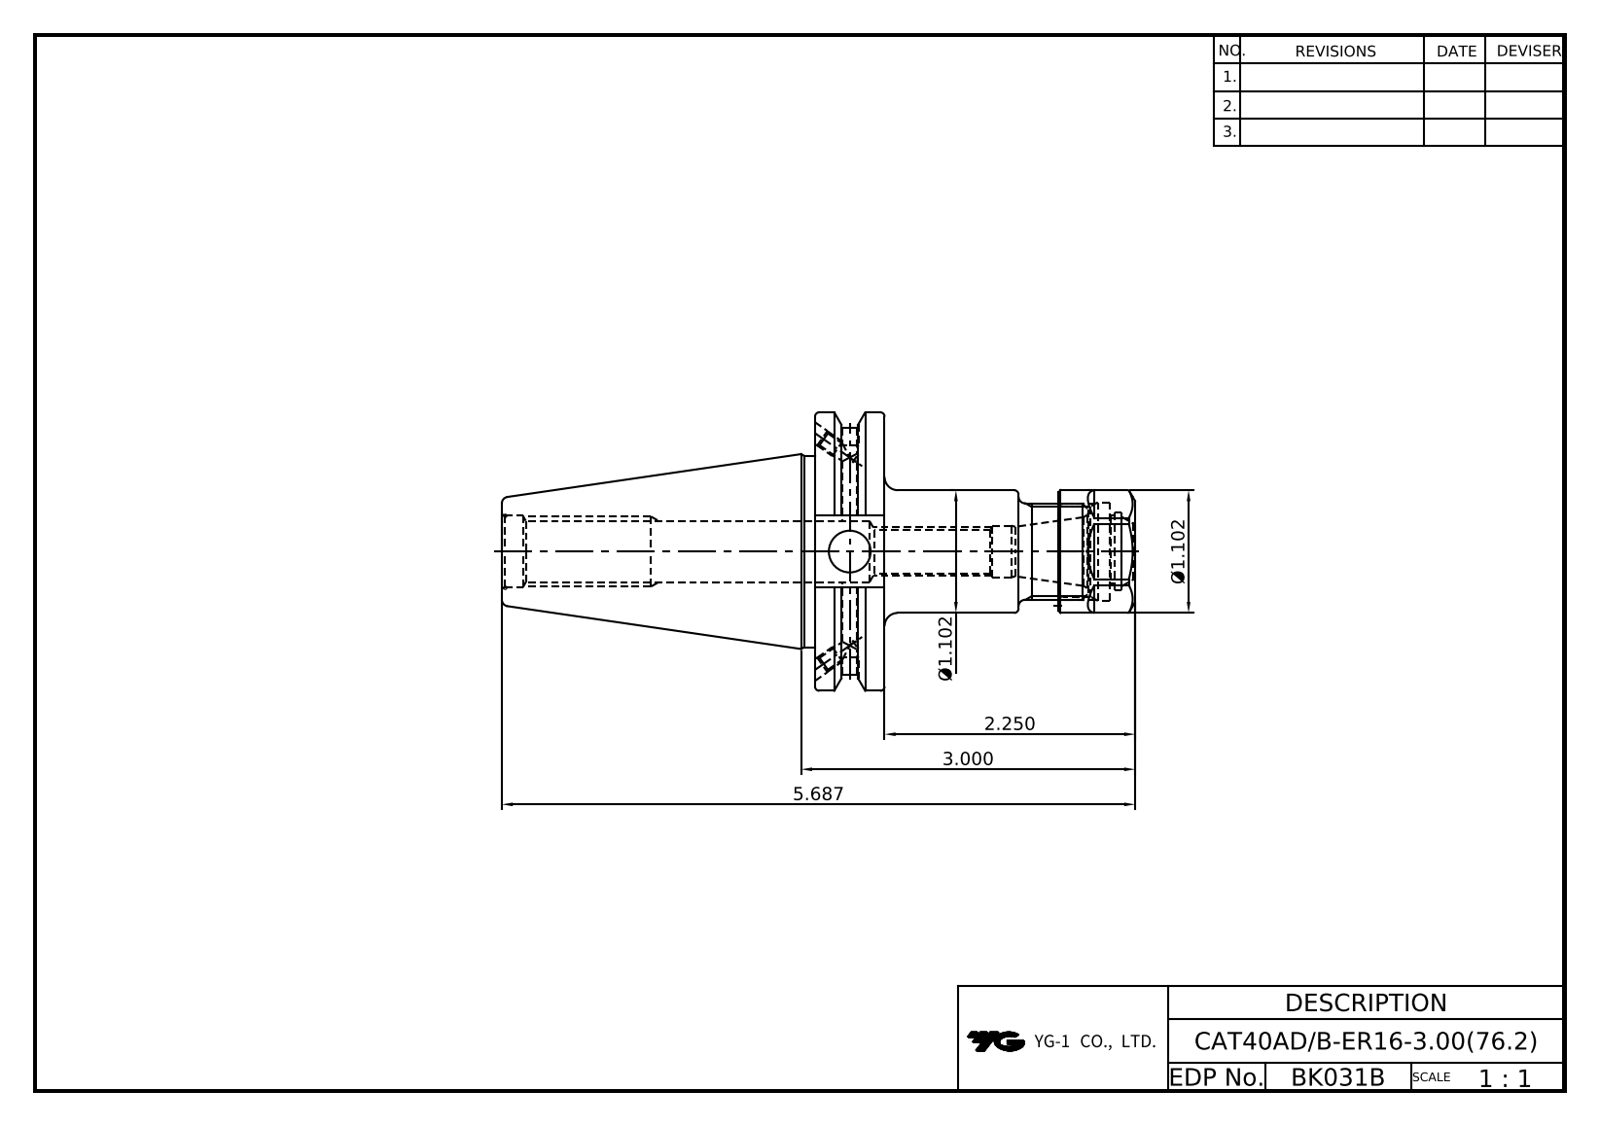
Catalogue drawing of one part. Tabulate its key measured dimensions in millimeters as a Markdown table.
| quantity | value |
| --- | --- |
| part name | LO-CAT40ADB-ER16-3.00; ER16NUT |
| STEP written by | Autodesk Inventor 2024 (AUTOMOTIVE_DESIGN) |
| units | millimeters |
| bodies | 2 solids, 123 faces (56 planar, 37 cylindrical, 30 other) |
| overall size | 144.45 × 63.5 × 61.09 |
| volume | 125 567 mm³ |
| surface area | 29 938 mm² |
| round holes (diameter × count) | 3.24 × 4, 4 × 2, 4.2 × 2, 1 × 1, 9.4 × 1, 9.53 × 1, 11.8 × 1, 12.8 × 1, 13.39 × 1, 16.3 × 1, 17.7 × 1, 20.6 × 1 |
| round bosses / shafts (diameter × count) | 63.5 × 1, 43.6 × 1, 28 × 1, 22 × 1 |
| partial cylindrical surfaces (radius × count) | 7.7 × 2, 28.15 × 1 |
| main face-to-face distances | 15.88, 25, 73.03, 57.15, 67.23, 51.35, 5.8, 47.6, 55.53, 39.65 |
| hole center spacings | 12 |
